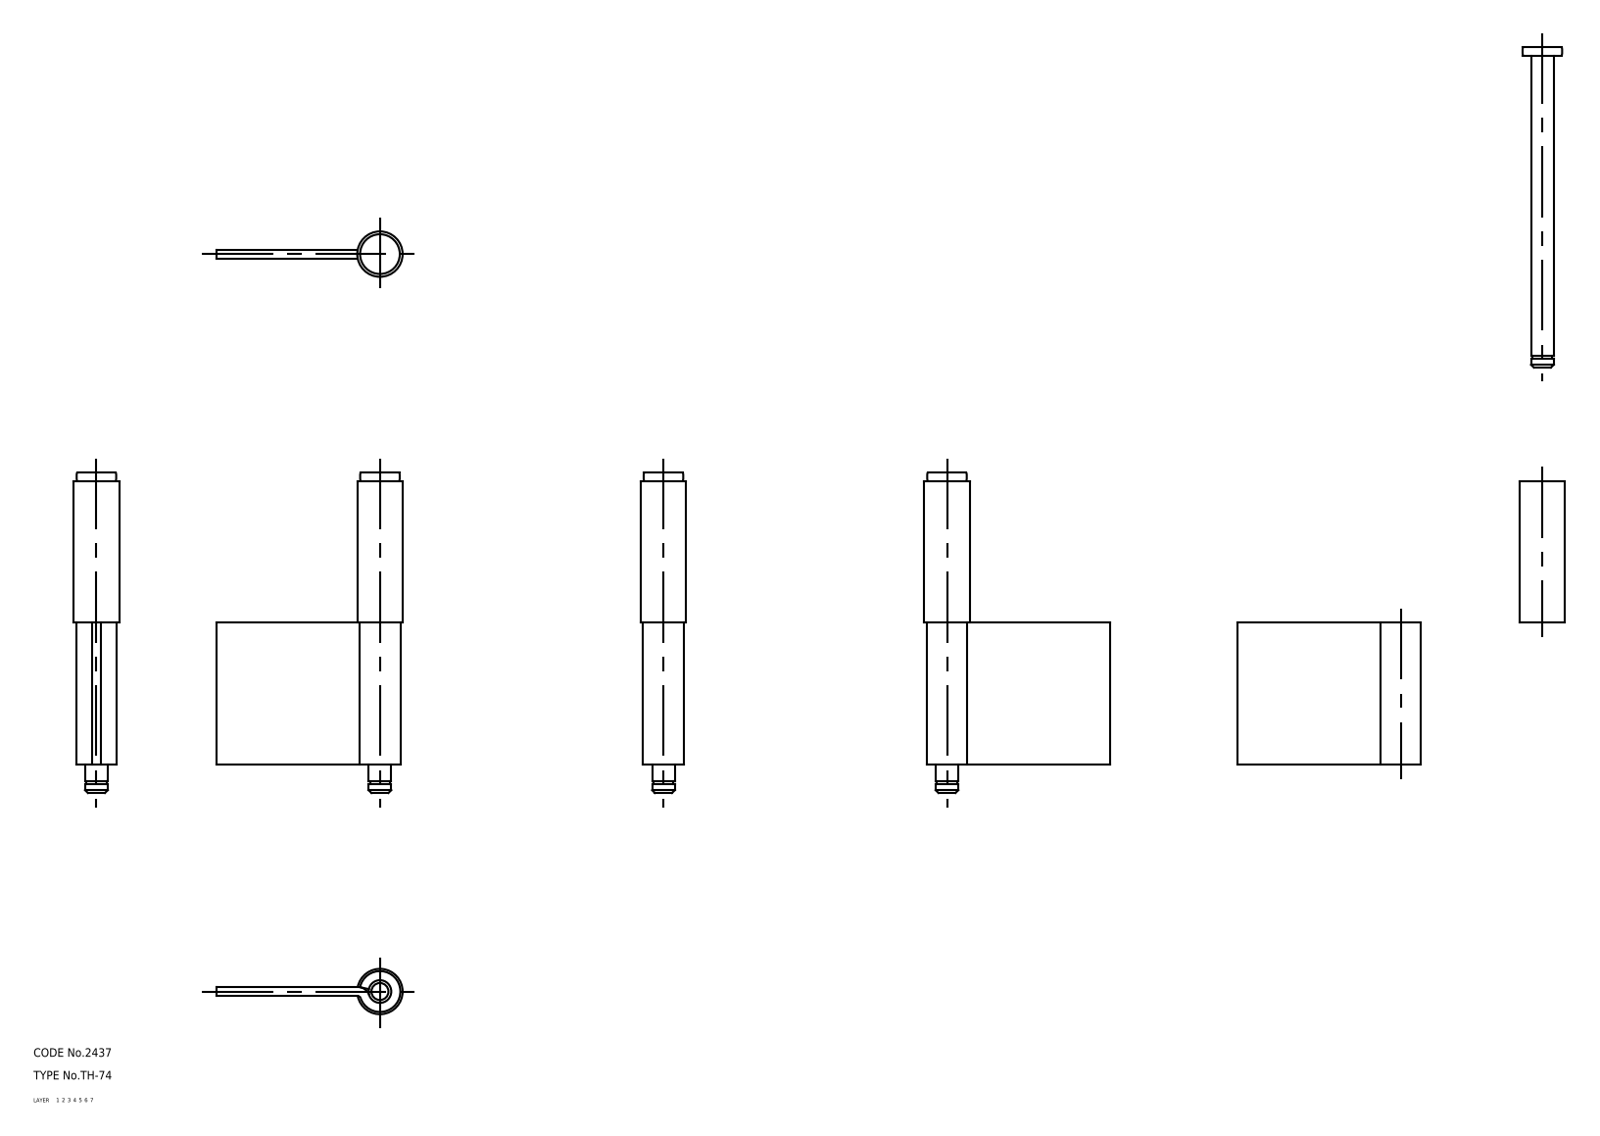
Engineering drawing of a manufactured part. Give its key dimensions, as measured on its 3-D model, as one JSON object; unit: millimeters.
{"part_name": "hinge piece_B; shaft; hinge piece_A; TH_74_14548_36", "step_written_by": "CADfix (AUTOMOTIVE_DESIGN)", "units": "millimeters", "bodies": {"solids": 3, "faces": 30, "planar": 0, "cylindrical": 0, "other": 30}, "overall_size": [113, 65.7, 16], "volume_mm3": 27173, "surface_area_mm2": 16669}
